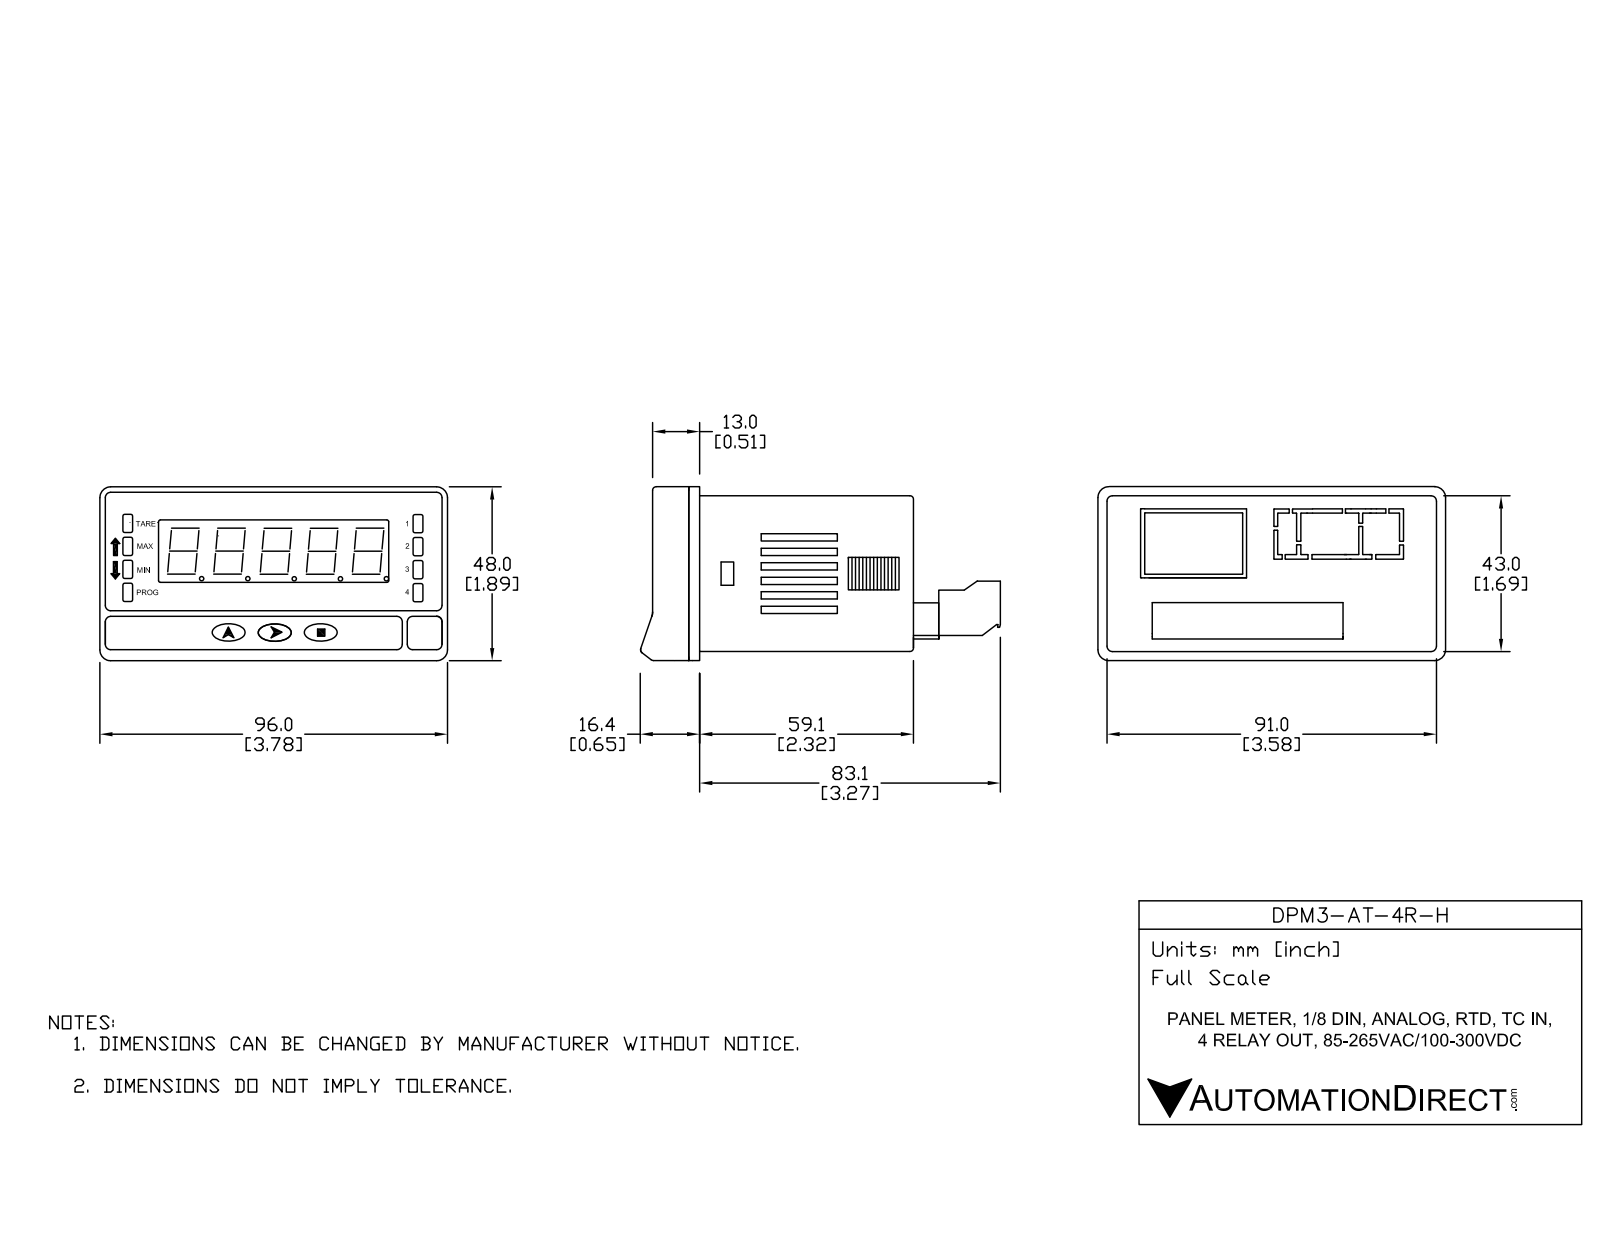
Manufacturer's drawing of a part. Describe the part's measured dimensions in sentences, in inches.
The part is named "DPM3-AT-4R-H". Its 3-D file was written by "SolidWorks 2017 (AUTOMOTIVE_DESIGN)". It is 10 solids with 2622 faces: 2041 planar, 368 cylindrical and 213 other. Overall it measures 3.916 by 3.78 by 1.89 inches. Its volume is 5.643 cubic inches and its surface area 104.7 square inches. Round holes: 12 of diameter 0.039, 12 of diameter 0.079, 10 of diameter 0.078, 10 of diameter 0.118, 10 of diameter 0.152. Round bosses or shafts: 5 of diameter 0.047. Partial cylindrical surfaces (rounded edges, fillets, slot ends): 53 of radius 0.004, 42 of radius 0.02, 24 of radius 0.012, 24 of radius 0.014, 12 of radius 0.07, 12 of radius 0.072, 10 of radius 0.118, 10 of radius 0.121. The main face-to-face distances are 0.059, 1.634, 0.098, 1.693, 1.575, 1.732, 3.524, 0.433, 0.157, 2.78. The hole center spacings are 0.138, 0.276, 0.201, 0.413, 0.748, 0.197, 0.197, 0.201.
